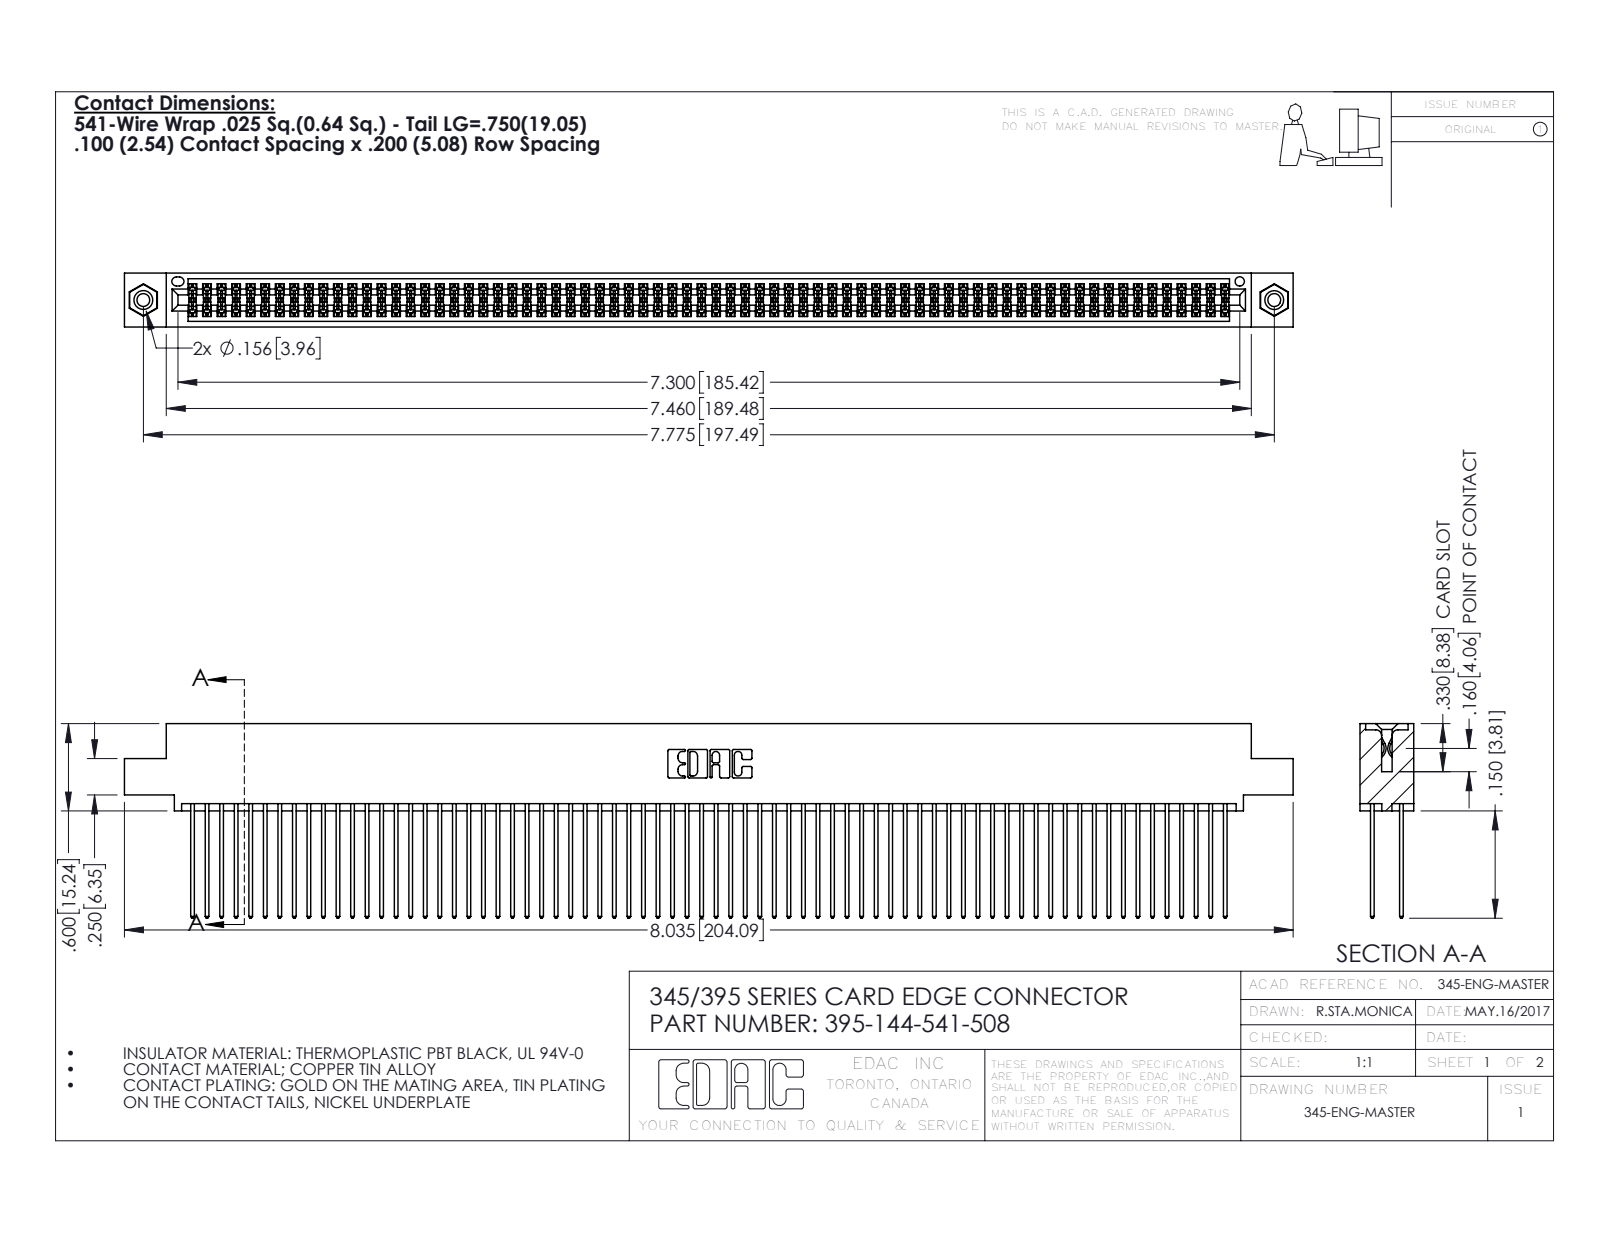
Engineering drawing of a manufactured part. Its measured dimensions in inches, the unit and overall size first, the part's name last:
Units: inches
Overall size (bounding box): 8.035 × 1.337 × 0.37
Round holes (diameter × count): ⌀0.089 ×2, ⌀0.125 ×2, ⌀0.156 ×2, ⌀0.064 ×1
Round bosses / shafts (diameter × count): ⌀0.155 ×2
Partial cylindrical surfaces — rounded edges, fillets, slot ends (radius × count): R0.006 ×216, R0.01 ×144, R0.01 ×22, R0.007 ×6, R0.031 ×6, R0.026 ×3, R0.014 ×2, R0.019 ×2
Main face-to-face distances: 0.072, 0.298, 0.2, 0.098, 0.272, 0.025, 0.225, 0.37, 0.175, 0.149
Hole centre spacings: 0.27, 7.539, 7.775
Volume: 1.272 in³ · Surface area: 54.86 in²
Bodies: 147 solids, 7390 faces (4868 planar, 2506 cylindrical, 16 other)
Part name (STEP PRODUCT): 395-144-541-508; 345 Part_0.110 Offset - 0.156 Dia-TI; 345-250-001_345-250-003-102; 345-292-001_345-293-141
STEP written by: SolidWorks 2016 (CONFIG_CONTROL_DESIGN)
